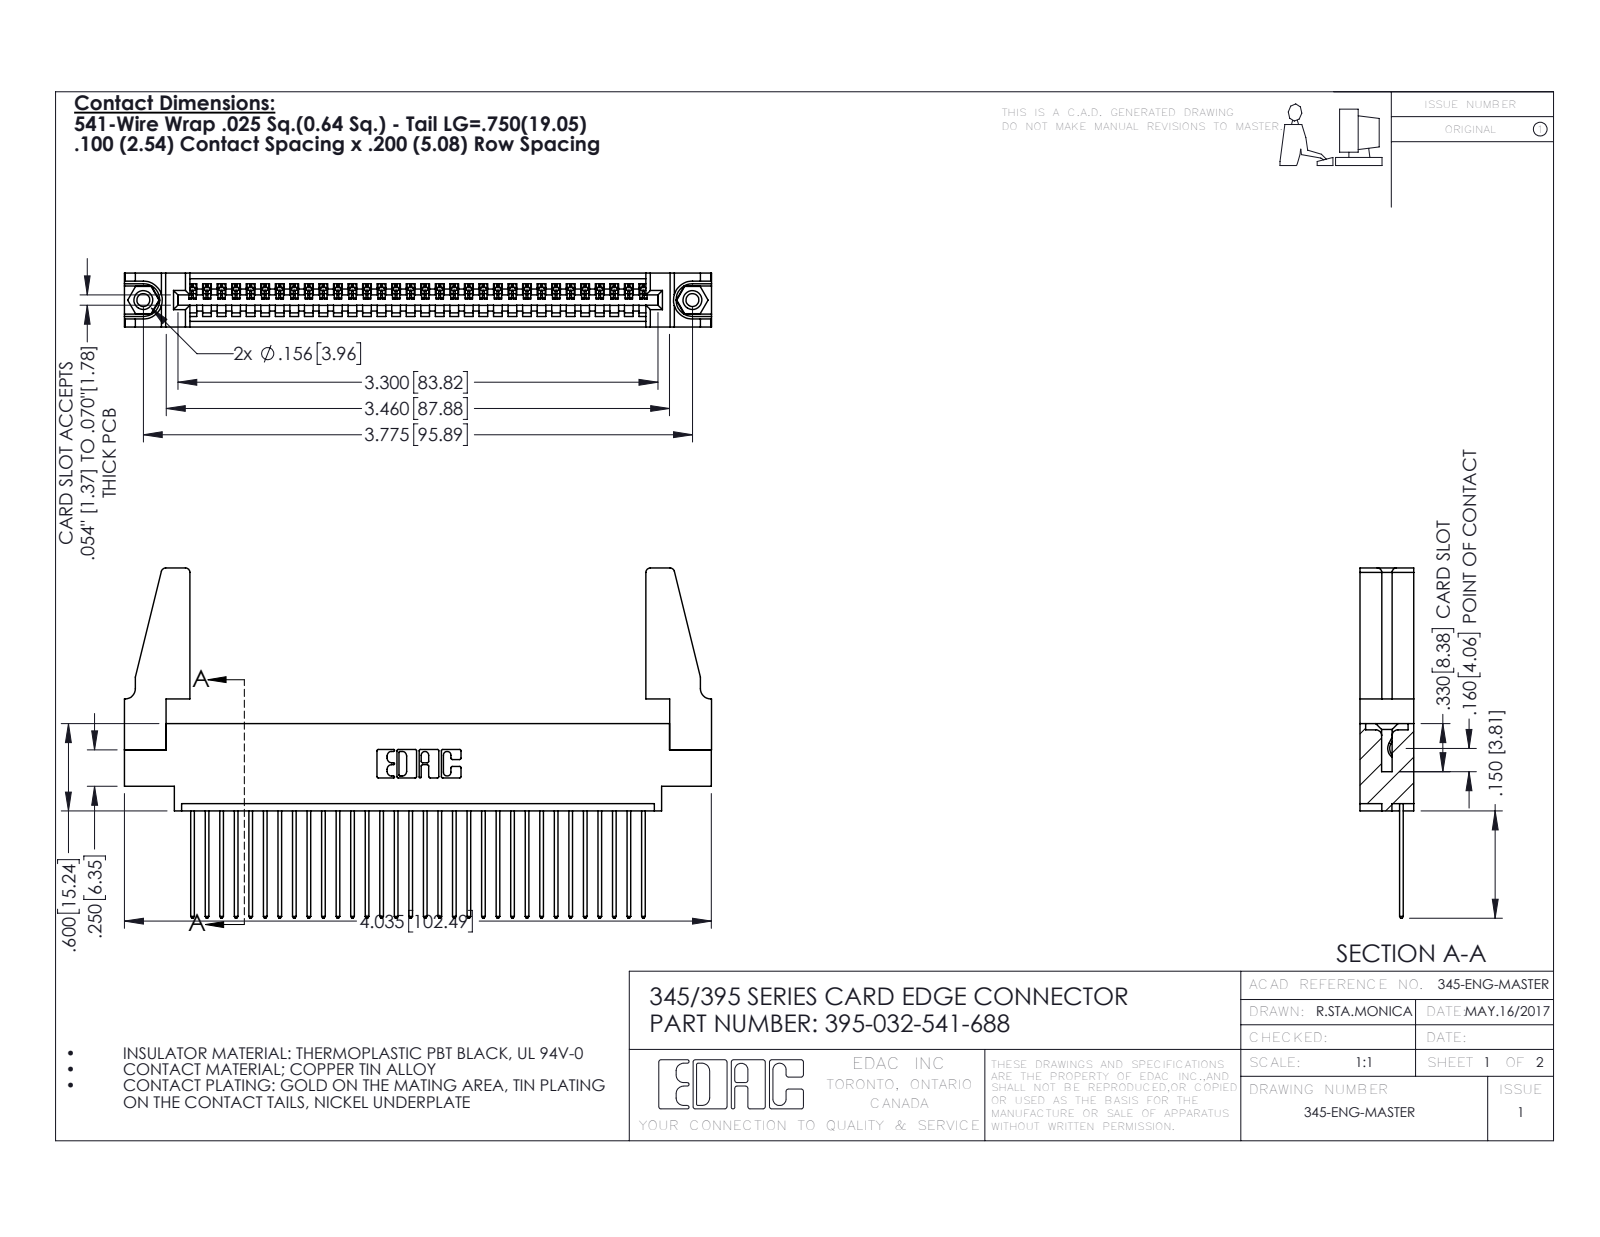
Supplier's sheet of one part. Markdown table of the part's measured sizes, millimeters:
| quantity | value |
| --- | --- |
| part name | 345-250-001_345-250-001-102; 395-032-541-688; 345-292-001_345-293-141; 345 Part_0.170 Offset - 0.156 Dia-TH (+1 more) |
| STEP written by | SolidWorks 2016 (CONFIG_CONTROL_DESIGN) |
| units | millimeters |
| bodies | 37 solids, 2110 faces (1436 planar, 658 cylindrical, 16 other) |
| overall size | 102.5 × 61.1 × 9.4 |
| volume | 12 900 mm³ |
| surface area | 16 560 mm² |
| round holes (diameter × count) | 2.3 × 2, 3.2 × 2, 4 × 2, 1.6 × 1 |
| round bosses / shafts (diameter × count) | 3.9 × 2 |
| partial cylindrical surfaces (radius × count) | 0.2 × 64, 0.3 × 64, 0.3 × 22, 0.8 × 8, 0.2 × 6, 0.8 × 6, 0.7 × 3, 0.8 × 2 |
| main face-to-face distances | 1.8, 7.6, 9.4, 2.5, 6.9, 0.6, 5.1, 5.7, 4.4, 3.8 |
| hole center spacings | 6.9, 89.9, 95.9 |
